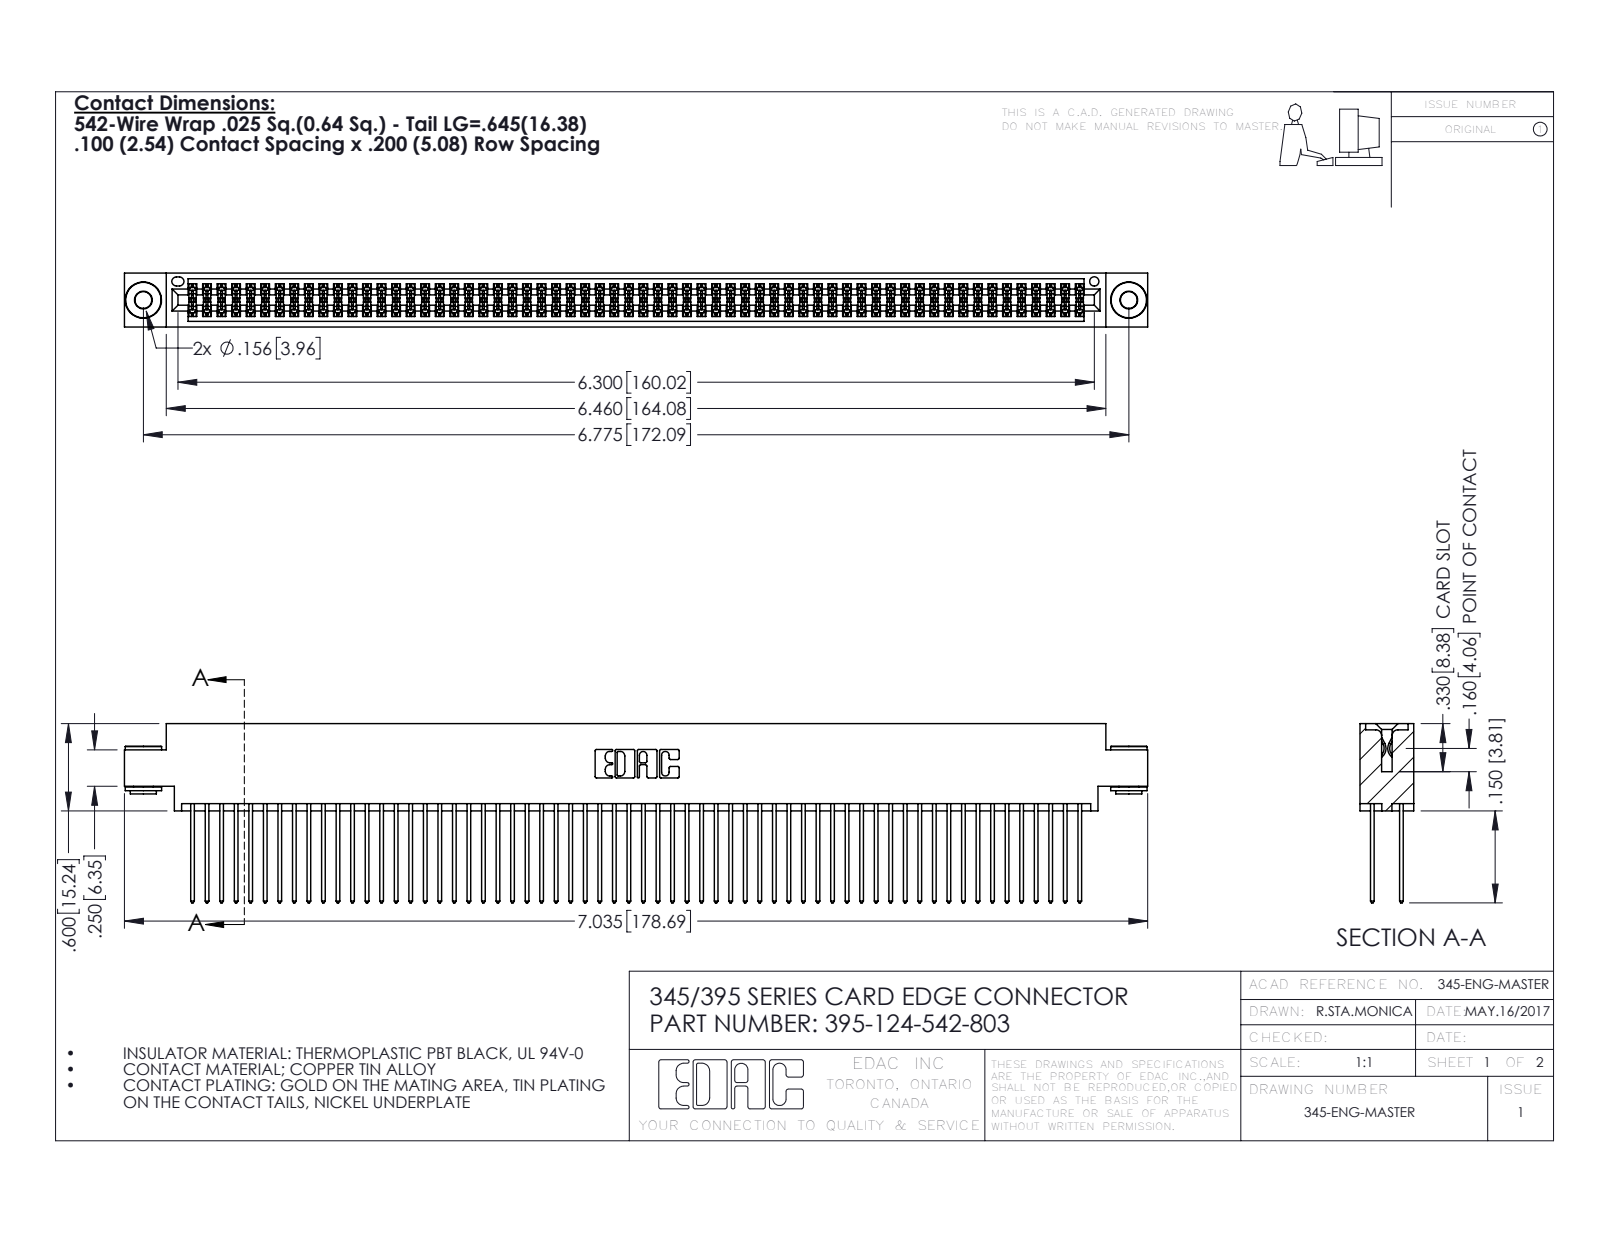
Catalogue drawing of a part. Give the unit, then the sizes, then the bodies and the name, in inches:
Units: inches
Overall size (bounding box): 7.035 × 1.232 × 0.37
Round holes (diameter × count): ⌀0.116 ×2, ⌀0.156 ×2, ⌀0.064 ×1
Round bosses / shafts (diameter × count): ⌀0.25 ×2, ⌀0.18 ×2, ⌀0.136 ×2
Partial cylindrical surfaces — rounded edges, fillets, slot ends (radius × count): R0.006 ×186, R0.01 ×124, R0.01 ×22, R0.007 ×6, R0.031 ×6, R0.026 ×3, R0.014 ×2, R0.019 ×2
Main face-to-face distances: 0.072, 0.298, 0.2, 0.098, 0.272, 0.025, 0.37, 0.225, 0.175, 0.149
Hole centre spacings: 0.27, 6.539, 6.775
Volume: 1.1 in³ · Surface area: 46.63 in²
Bodies: 127 solids, 6368 faces (4186 planar, 2174 cylindrical, 8 other)
Part name (STEP PRODUCT): 345-292-001_345-293-142; 345-250-002_345-250-002-102; 345 Part_0.170 Offset - 0.156 Dia-TH; 395-124-542-803
STEP written by: SolidWorks 2016 (CONFIG_CONTROL_DESIGN)
